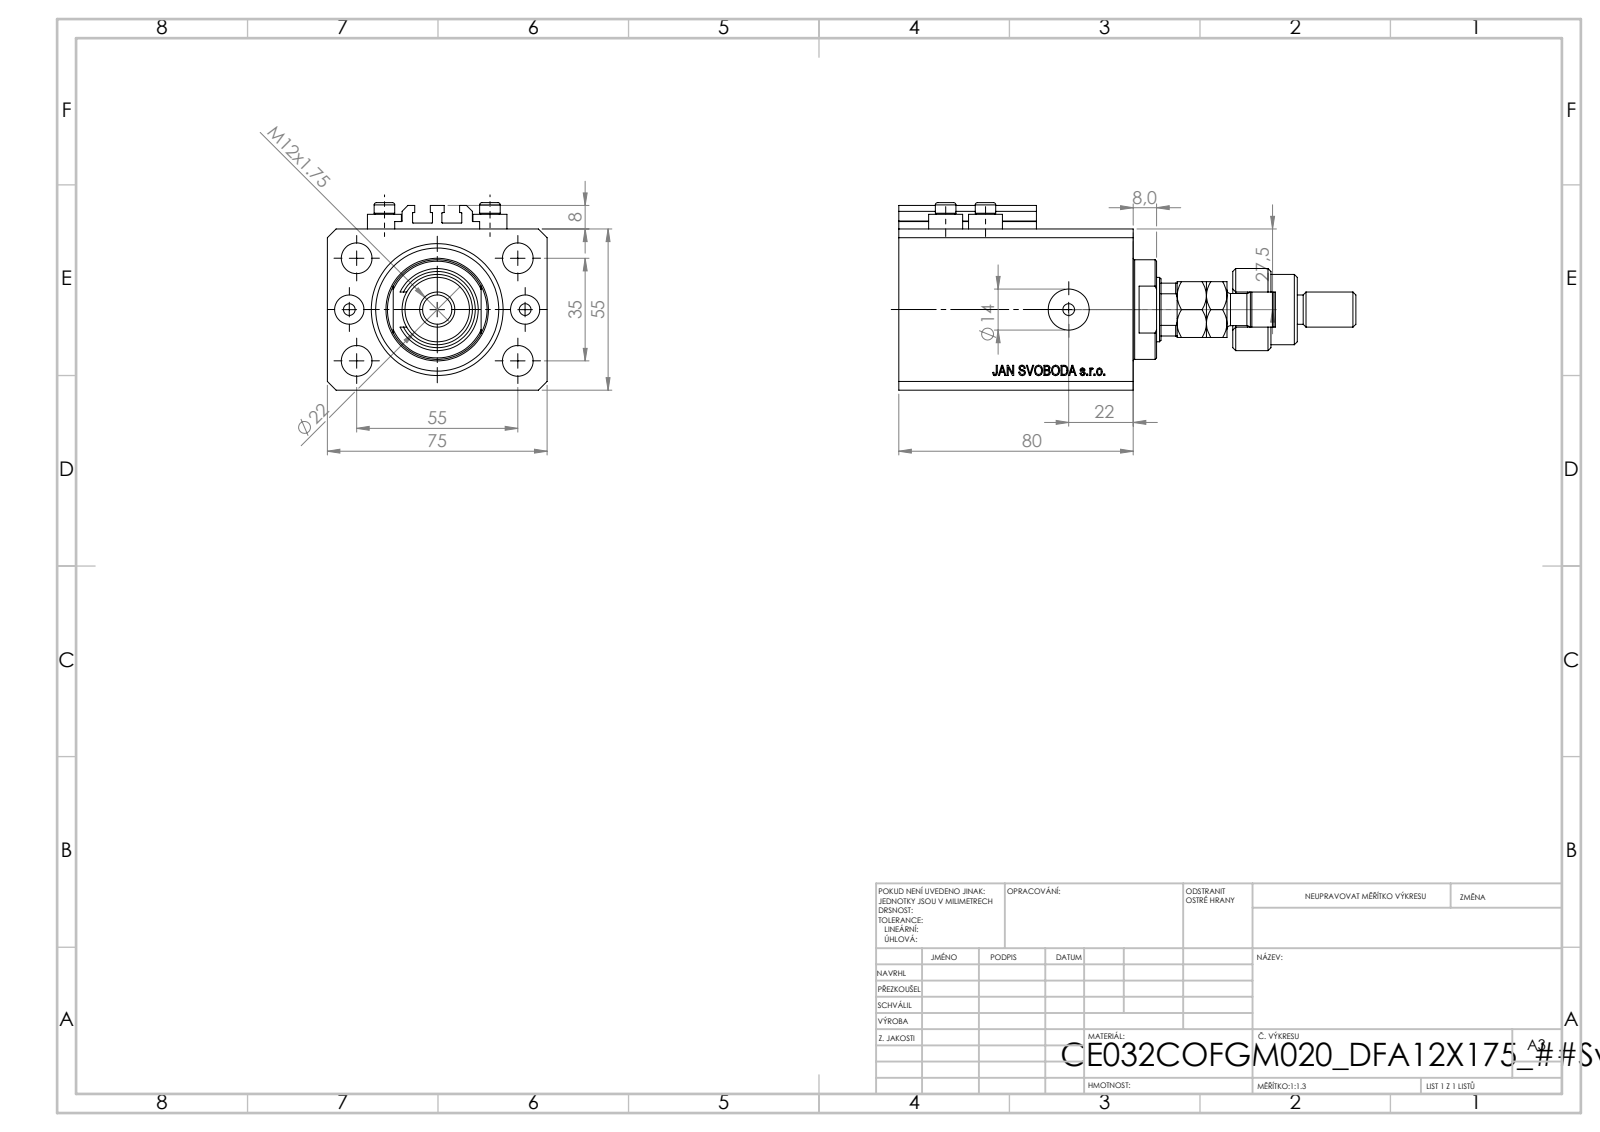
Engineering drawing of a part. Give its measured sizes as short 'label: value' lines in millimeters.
name: V250CE_C_Body; FEMALE_PART_FOR_DFA; ALLEN BOLT V250CE; V250CE_VC_C (+2 more)
written by: SolidWorks 2019 (CONFIG_CONTROL_DESIGN)
unit: mm
bodies: 10 solids, 1119 faces (532 planar, 99 cylindrical, 488 other)
size: 156 × 75 × 64
volume: 322 930 mm³; area: 78 578 mm²
holes: 8× ⌀4, 5× ⌀10.5, 2× ⌀10, 2× ⌀14, 1× ⌀22, 1× ⌀32, 1× ⌀45
bosses: 4× ⌀11.6, 4× ⌀7, 1× ⌀34, 1× ⌀28, 1× ⌀24, 1× ⌀18, 1× ⌀12, 1× ⌀11
rounds: 10× R0.2, 1× R9.75, 1× R10.5
face distances: 55, 75, 15, 80, 65, 9.9, 55.1, 70.1, 8, 3
hole spacings: 17.68, 32.6, 60.1, 36, 13.6, 30, 35, 38.48
